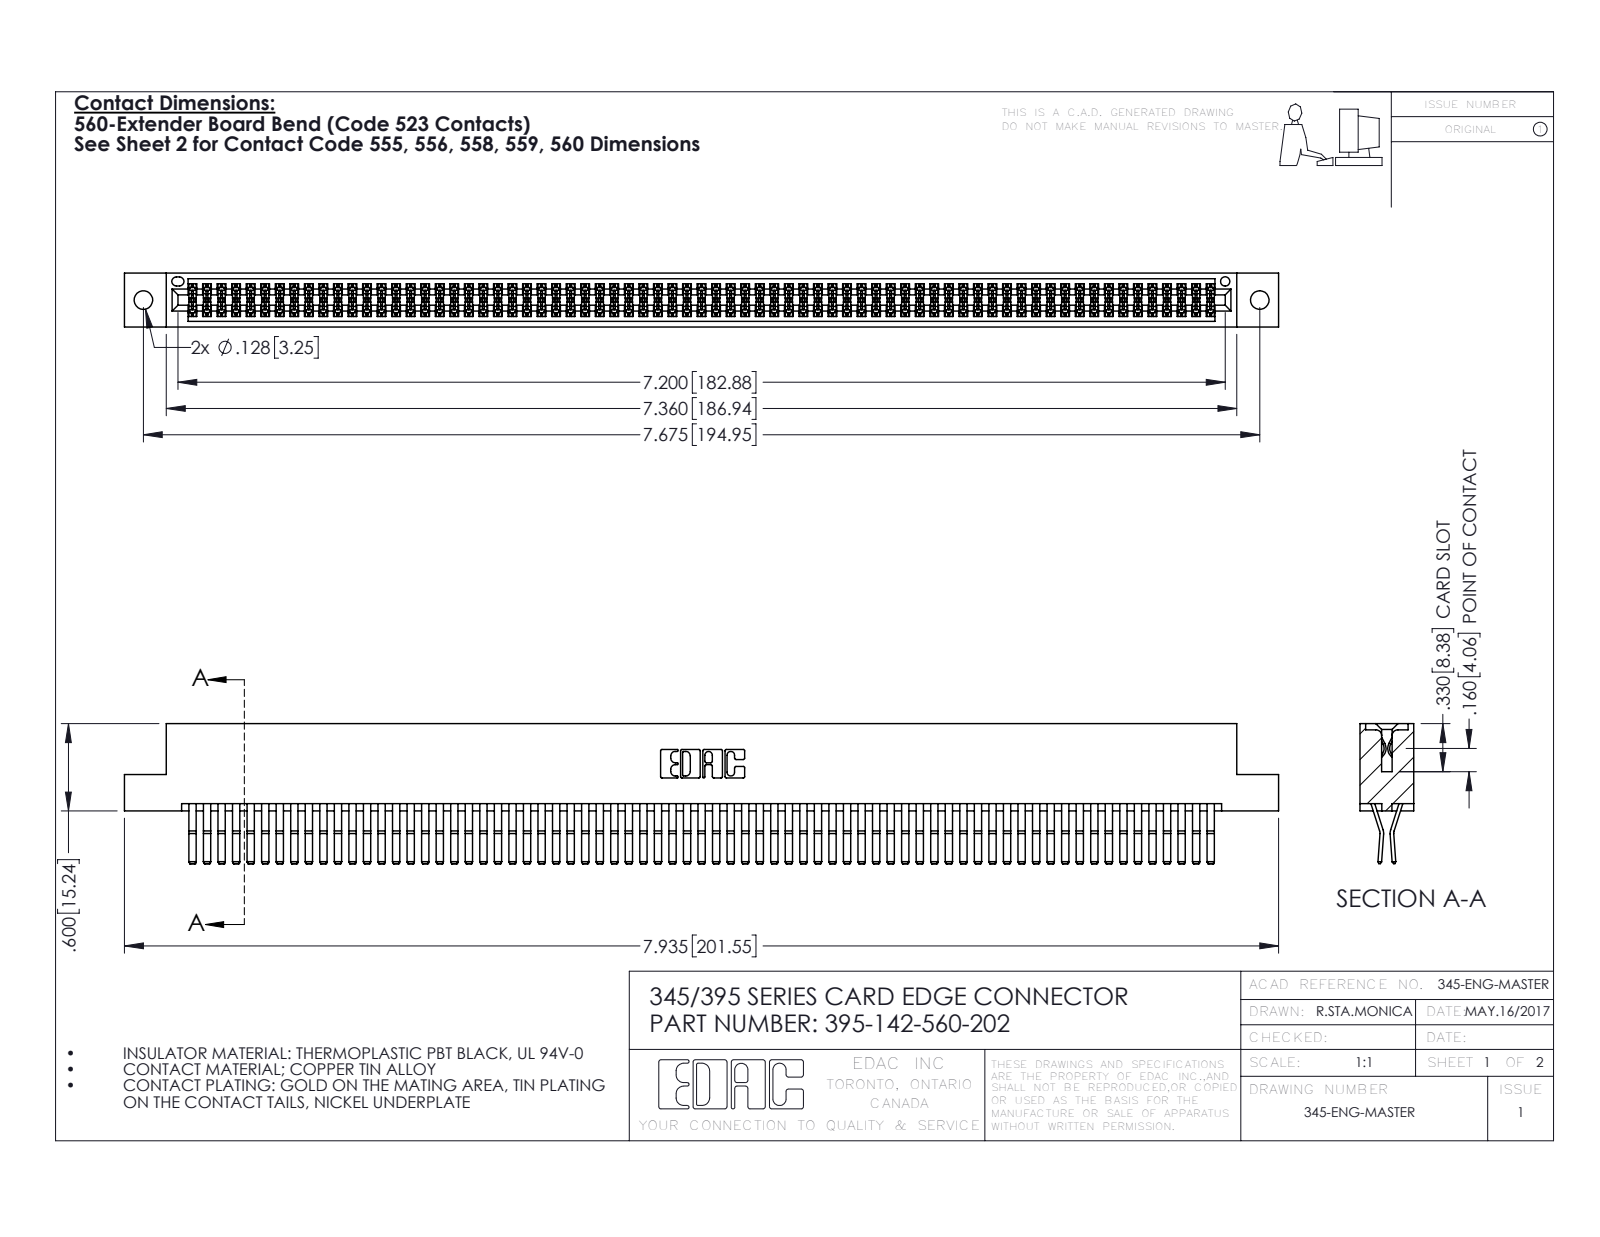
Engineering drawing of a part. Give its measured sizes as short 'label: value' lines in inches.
name: 345-292-001_560 Tail; 345 Part_Flush Mounting Lugs - 0.128 Dia; 395-142-560-202
written by: SolidWorks 2016 (CONFIG_CONTROL_DESIGN)
unit: in
bodies: 143 solids, 7510 faces (4766 planar, 2744 cylindrical, 0 other)
size: 7.935 × 0.962 × 0.37
volume: 1.266 in³; area: 51.68 in²
holes: 2× ⌀0.128, 1× ⌀0.064
rounds: 213× R0.006, 22× R0.01, 6× R0.007, 6× R0.031, 3× R0.026, 2× R0.01, 2× R0.014, 2× R0.019
face distances: 0.025, 0.298, 0.072, 0.37, 0.2, 0.098, 0.272, 0.225, 0.175, 0.149
hole spacings: 0.27, 7.439, 7.675
